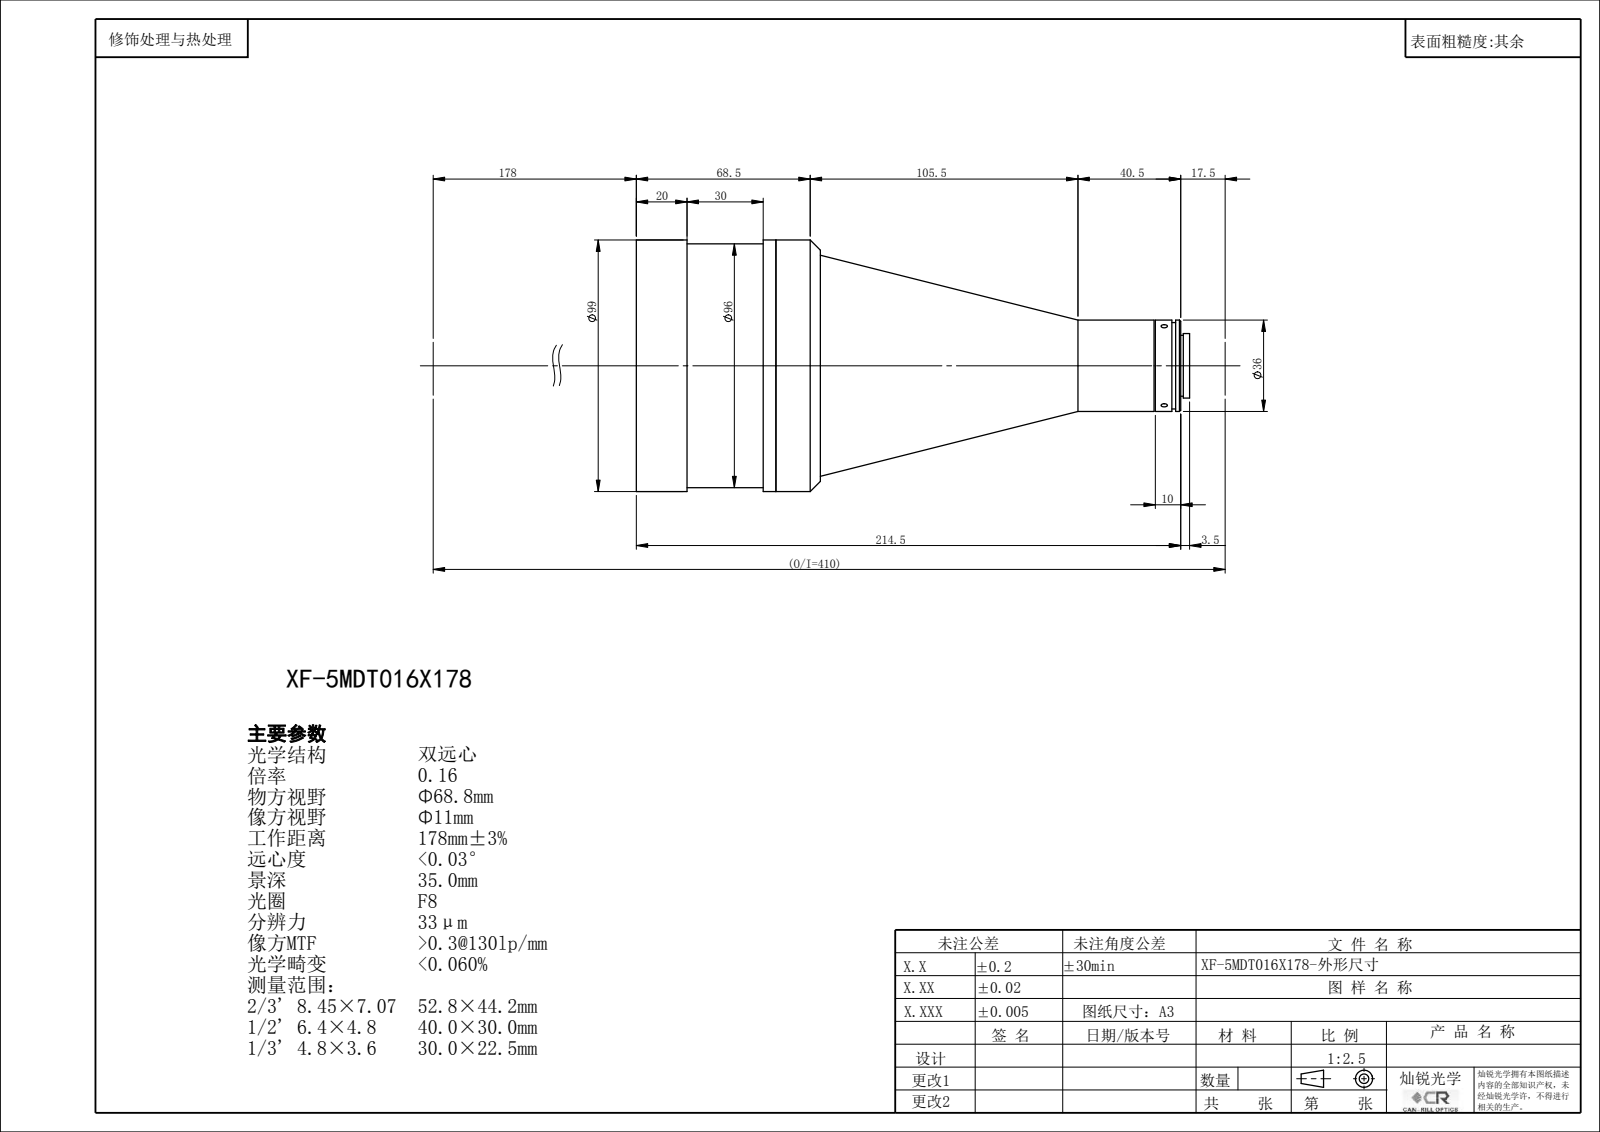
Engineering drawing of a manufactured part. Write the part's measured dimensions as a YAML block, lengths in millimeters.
part_name: "XF-5MDT016X178"
step_written_by: "SolidWorks 2014 (CONFIG_CONTROL_DESIGN)"
units: millimeters
bodies: {solids: 0, faces: 96, planar: 38, cylindrical: 44, other: 14}
overall_size: [217.96, 99, 99]
round_holes:
  - {diameter: 2.5, count: 3}
  - {diameter: 2, count: 2}
  - {diameter: 16, count: 1}
  - {diameter: 19.2, count: 1}
  - {diameter: 21.4, count: 1}
  - {diameter: 85, count: 1}
  - {diameter: 87, count: 1}
  - {diameter: 92, count: 1}
round_bosses_or_shafts:
  - {diameter: 99, count: 1}
  - {diameter: 96, count: 1}
  - {diameter: 36, count: 1}
  - {diameter: 34, count: 1}
  - {diameter: 25.4, count: 1}
  - {diameter: 24, count: 1}
face_to_face_distances: [55, 5, 9.53, 45.47, 72.5, 62.97, 17.5, 214.46, 204.93, 159.46]
hole_center_spacings: [11.5, 23]
